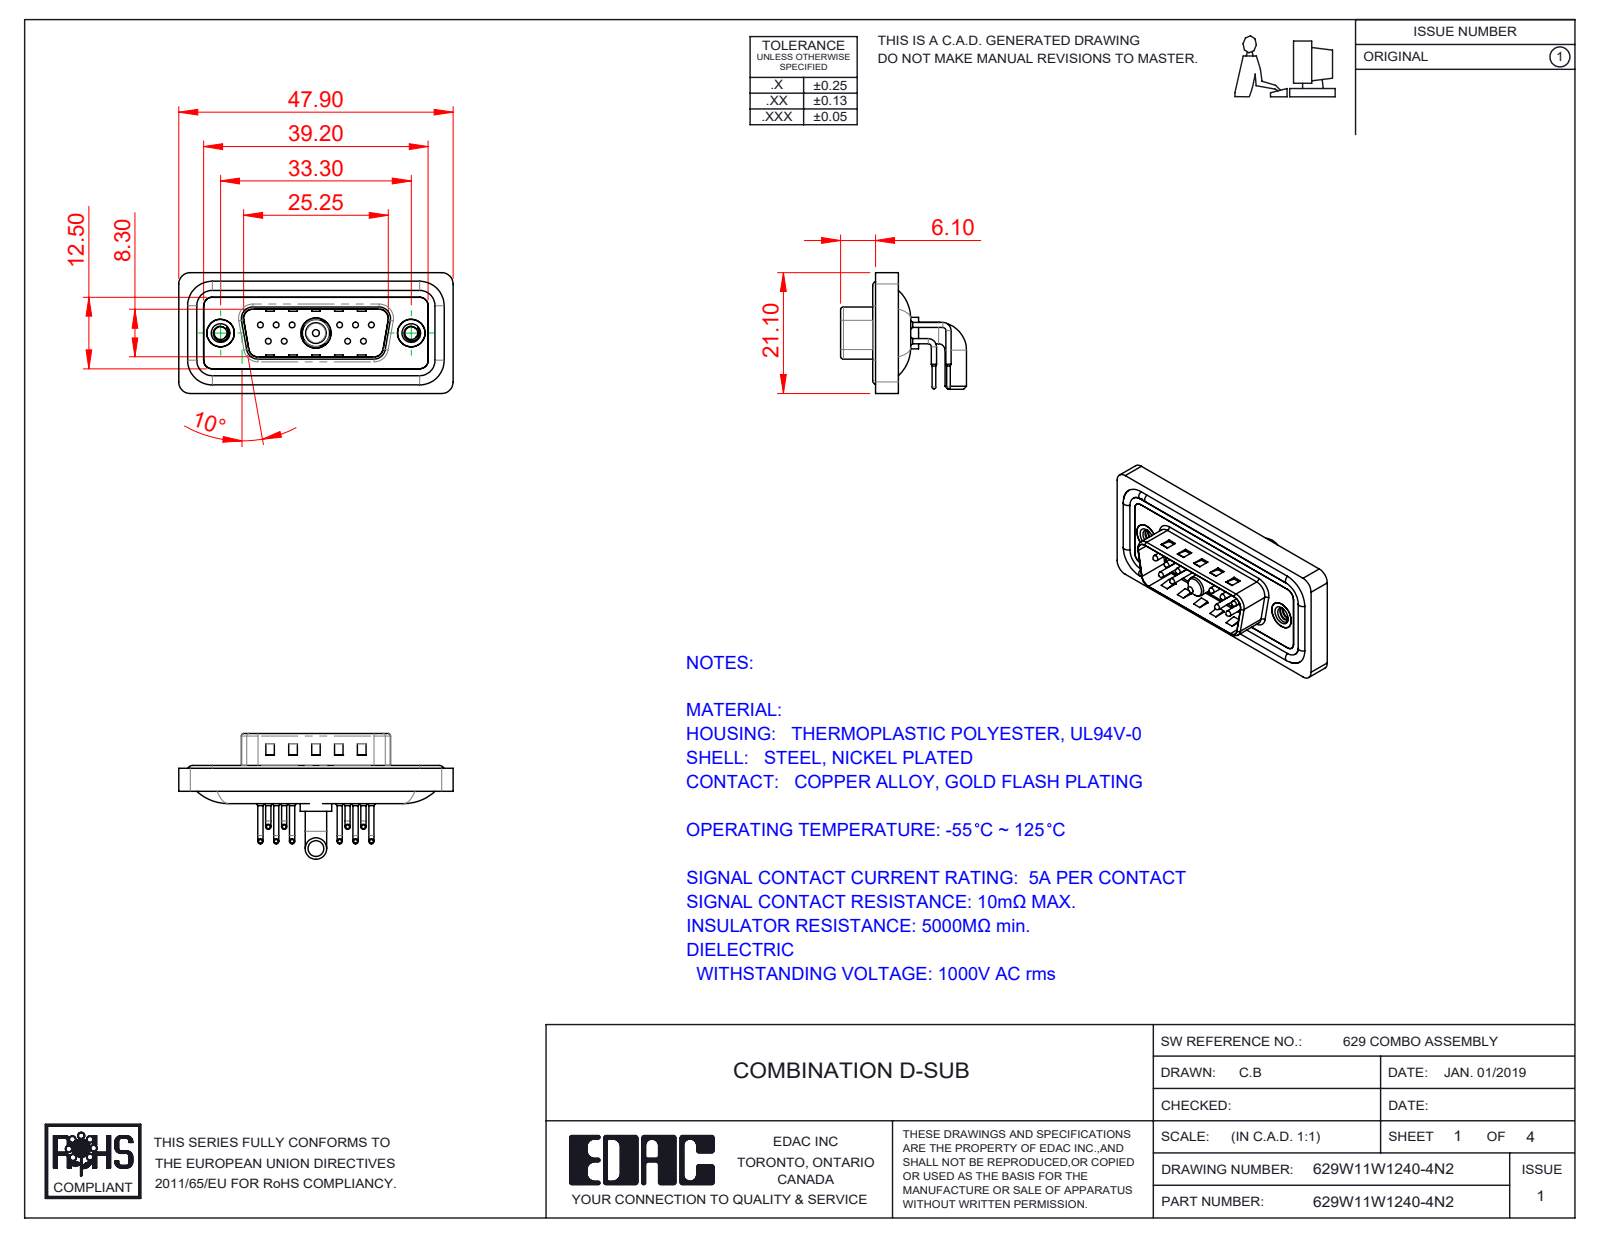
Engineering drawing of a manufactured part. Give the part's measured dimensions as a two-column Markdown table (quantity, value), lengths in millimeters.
| quantity | value |
| --- | --- |
| part name | 629Combo Waterproof Housing_15 Contacts; 629W11W1240-4N2; 629Combo Shell Front_15 Contacts; Power Pin_40A RA (+5 more) |
| STEP written by | SolidWorks 2020 (CONFIG_CONTROL_DESIGN) |
| units | millimeters |
| bodies | 19 solids, 1603 faces (836 planar, 569 cylindrical, 198 other) |
| overall size | 47.9 × 21.98 × 21.1 |
| volume | 5 673 mm³ |
| surface area | 9 324 mm² |
| round holes (diameter × count) | 0.75 × 10, 1.6 × 10, 2 × 10, 2.26 × 2, 4 × 2, 4.8 × 2, 5 × 2, 4.85 × 1, 5.3 × 1 |
| round bosses / shafts (diameter × count) | 0.9 × 20, 1.5 × 10, 1 × 10, 0.65 × 10, 1.6 × 4, 4.9 × 2, 3.75 × 2, 5.5 × 1 |
| partial cylindrical surfaces (radius × count) | 2 × 20, 1.5 × 18, 1.01 × 10, 0.5 × 8, 1.6 × 8, 1 × 7, 0.25 × 4, 0.6 × 4 |
| main face-to-face distances | 0.4, 2.9, 0.8, 1.1, 2.1, 1.6, 2.5, 4.1, 4.5, 3.1 |
| hole center spacings | 3.16, 2.77, 13.85, 11.08, 16.62, 5.03, 5.04, 5.54 |
